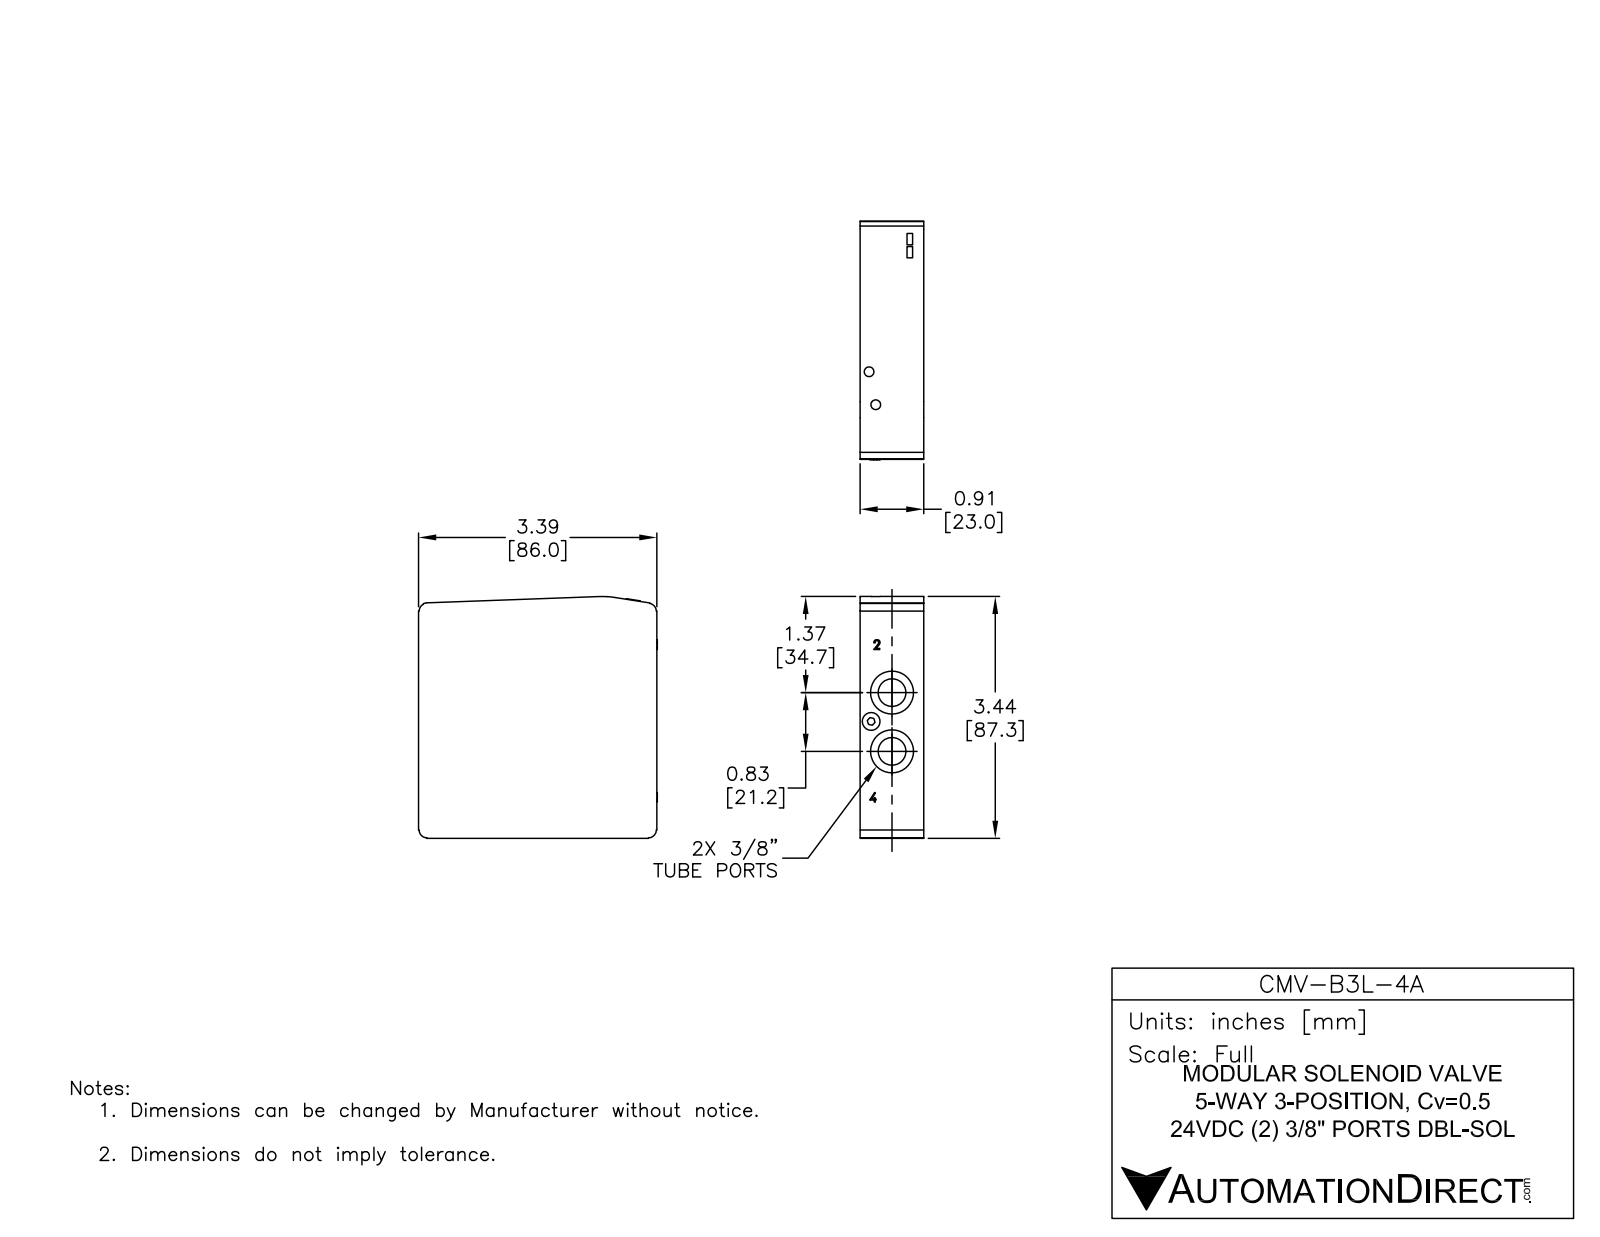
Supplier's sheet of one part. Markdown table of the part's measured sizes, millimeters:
| quantity | value |
| --- | --- |
| part name | CMV-B3L-4A |
| STEP written by | SolidWorks 2013 (AUTOMOTIVE_DESIGN) |
| units | millimeters |
| bodies | 74 solids, 1155 faces (887 planar, 159 cylindrical, 109 other) |
| overall size | 89.5 × 87.3 × 31.43 |
| volume | 154 043 mm³ |
| surface area | 54 268 mm² |
| round holes (diameter × count) | 4.4 × 4, 5.25 × 4, 6.5 × 2, 9.75 × 2, 14 × 2, 18 × 2, 3.35 × 1, 3.6 × 1, 6.25 × 1, 6.4 × 1 |
| round bosses / shafts (diameter × count) | 4 × 4, 1.5 × 4, 15.25 × 2, 11 × 2, 6.25 × 2, 5.75 × 2, 4.2 × 2, 3.5 × 1 |
| partial cylindrical surfaces (radius × count) | 2.35 × 12, 0.78 × 4, 1.5 × 4, 2.8 × 4, 0.15 × 2, 0.25 × 2, 1 × 2, 0.17 × 1 |
| main face-to-face distances | 22.5, 12.5, 10, 83, 3, 1, 65.12, 50.25, 32.75, 53.25 |
| hole center spacings | 9.7, 11.99, 12.17, 16, 22.17, 31.45, 31.52, 39.5 |
